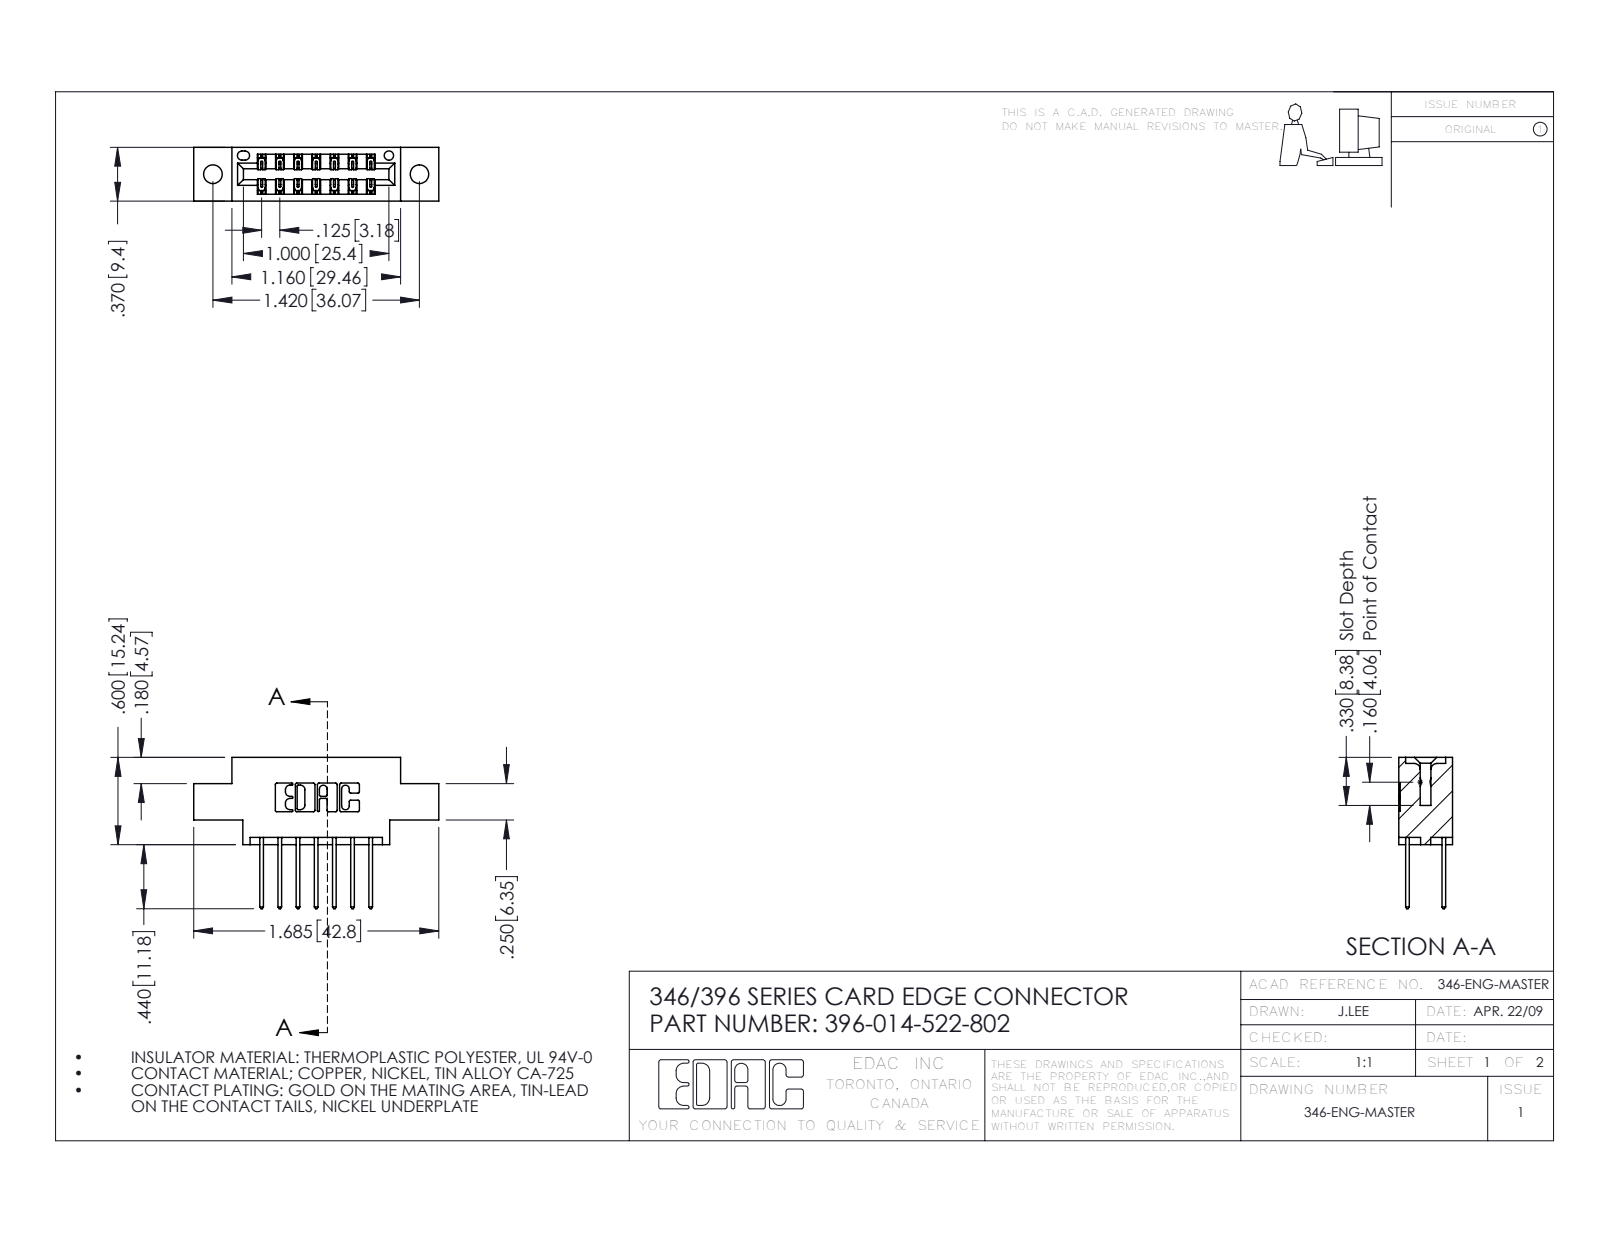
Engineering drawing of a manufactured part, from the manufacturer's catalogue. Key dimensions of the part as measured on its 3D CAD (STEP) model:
Part name (STEP PRODUCT): 396-014-522-802; 345-292-001_345-293-122; 346 Part_0.170 Offset - 0.128 Dia
STEP written by: SolidWorks 2016 (CONFIG_CONTROL_DESIGN)
Units: inches
Bodies: 15 solids, 854 faces (570 planar, 284 cylindrical, 0 other)
Overall size (bounding box): 1.685 × 1.04 × 0.37
Volume: 0.229 in³ · Surface area: 7.248 in²
Round holes (diameter × count): ⌀0.128 ×2, ⌀0.064 ×1
Partial cylindrical surfaces — rounded edges, fillets, slot ends (radius × count): R0.01 ×22, R0.006 ×21, R0.01 ×14, R0.007 ×6, R0.031 ×6, R0.026 ×3, R0.014 ×2, R0.022 ×2
Main face-to-face distances: 0.25, 0.37, 0.048, 0.322, 0.072, 0.298, 0.025, 0.275, 0.225, 0.148
Hole centre spacings: 0.246, 1.217, 1.42
